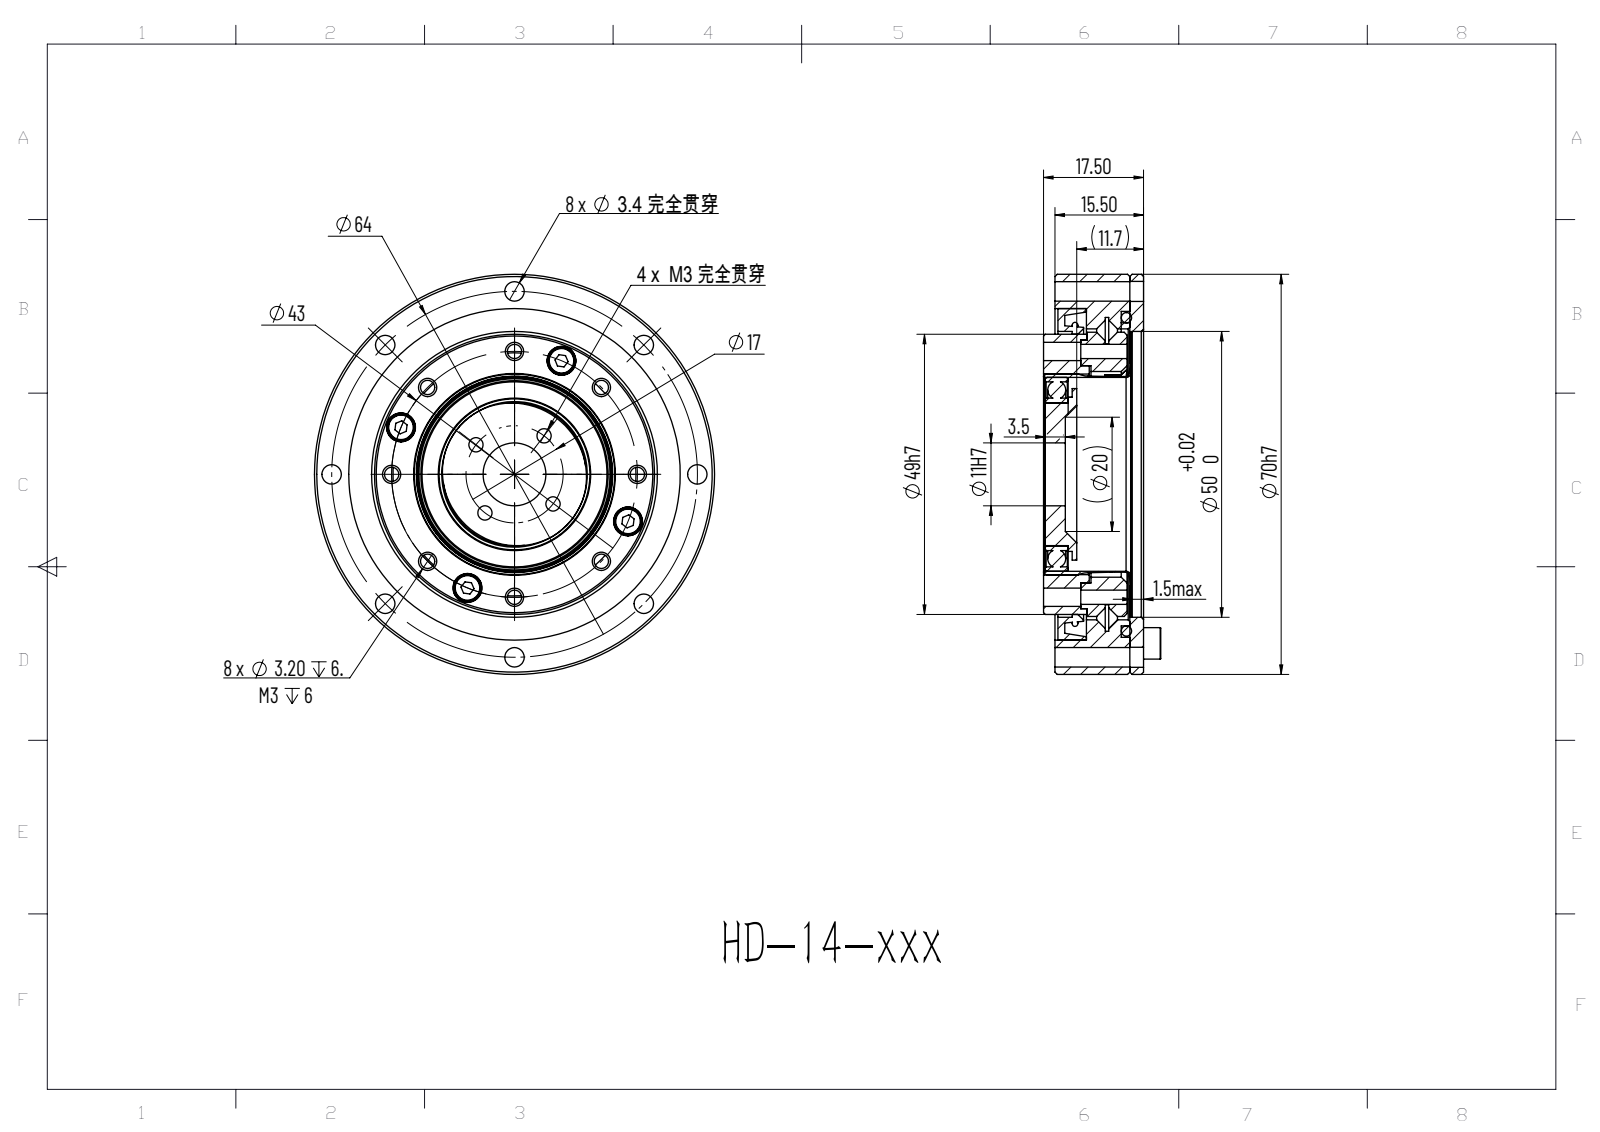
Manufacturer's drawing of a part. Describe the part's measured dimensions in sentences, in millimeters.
The part is named "HD-14-xxx; ??HD-14; HD-14-??; HD-14????_?? <1> (+4 more)". Its 3-D file was written by "ONSHAPE BY PTC INC, 1.201 (AP242_MANAGED_MODEL_BASED_3D_ENGINEERING_MIM_LF)". It is 15 solids with 306 faces: 118 planar, 105 cylindrical and 83 other. Overall it measures 70 by 70 by 20.5 millimeters. Its volume is 40 825 cubic millimeters and its surface area 39 544 square millimeters. Round holes: 14 of diameter 2.5, 10 of diameter 3.5, 8 of diameter 3.2, 8 of diameter 3.4, 4 of diameter 2.05, 4 of diameter 2.7, 4 of diameter 5, 1 of diameter 1.6, 1 of diameter 2.4, 1 of diameter 4.3, 1 of diameter 11, 1 of diameter 25.07. Round bosses or shafts: 4 of diameter 4.5, 4 of diameter 2.5, 2 of diameter 5.5, 2 of diameter 3, 1 of diameter 70, 1 of diameter 53, 1 of diameter 49.7, 1 of diameter 45.68. The main face-to-face distances are 0.5, 2.4, 5.5, 12.6, 7.1, 7.6, 6.5, 5, 2.5, 10. The hole center spacings are 38.55, 49.59, 22.66, 21.5, 10.5, 52.51, 53.5, 23.89.
